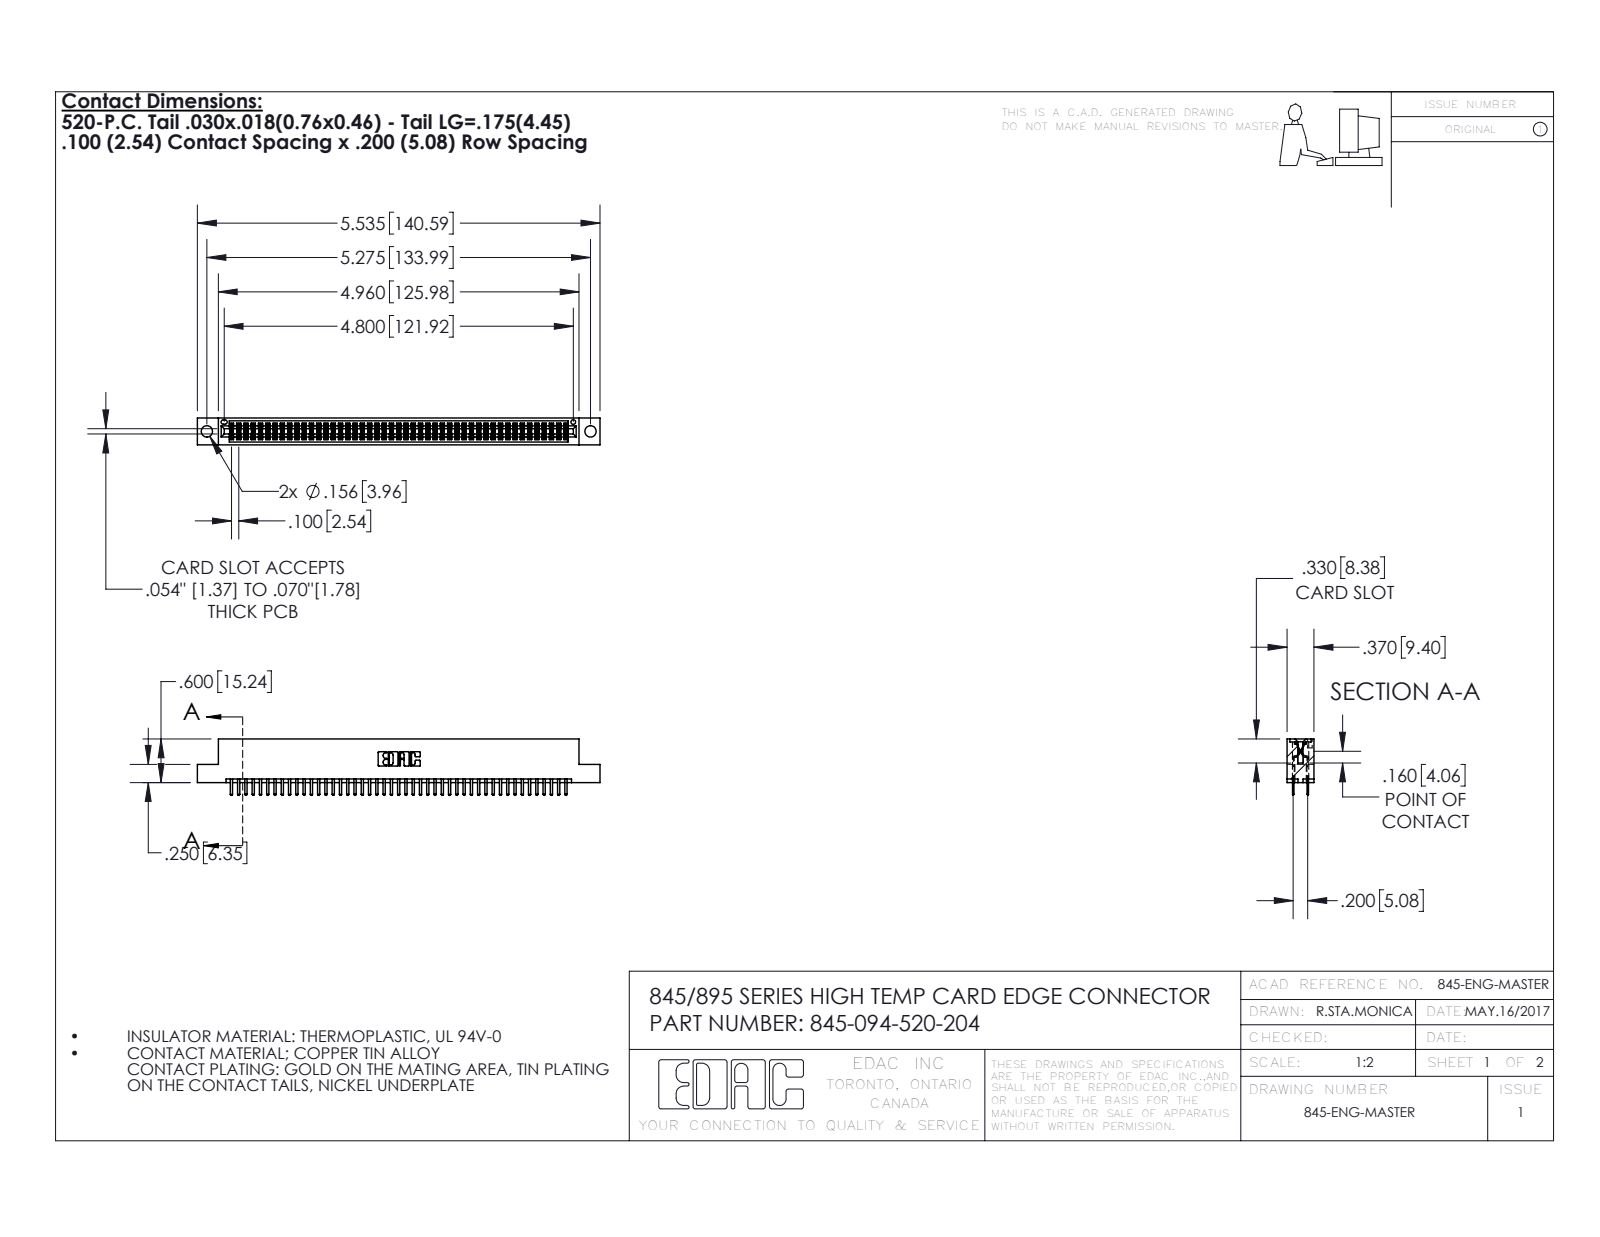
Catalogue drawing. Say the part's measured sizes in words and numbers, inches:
The part is named "345 Part_Flush Mounting Lugs - 0.156 Dia-TH; 345-094-520-204; 345-292-001_345-293-120". Its 3-D file was written by "SolidWorks 2016 (CONFIG_CONTROL_DESIGN)". It is 95 solids with 5202 faces: 3370 planar, 1832 cylindrical and 0 other. Overall it measures 5.535 by 0.775 by 0.37 inches. Its volume is 0.828 cubic inches and its surface area 30.83 square inches. Round holes: 2 of diameter 0.156, 1 of diameter 0.064. Partial cylindrical surfaces (rounded edges, fillets, slot ends): 141 of radius 0.006, 98 of radius 0.01, 22 of radius 0.01, 6 of radius 0.007, 6 of radius 0.031, 3 of radius 0.026, 2 of radius 0.014, 2 of radius 0.019. The main face-to-face distances are 0.298, 0.072, 0.2, 0.37, 0.098, 0.272, 0.025, 0.225, 0.022, 0.072. The hole center spacings are 0.27, 5.039, 5.275.
